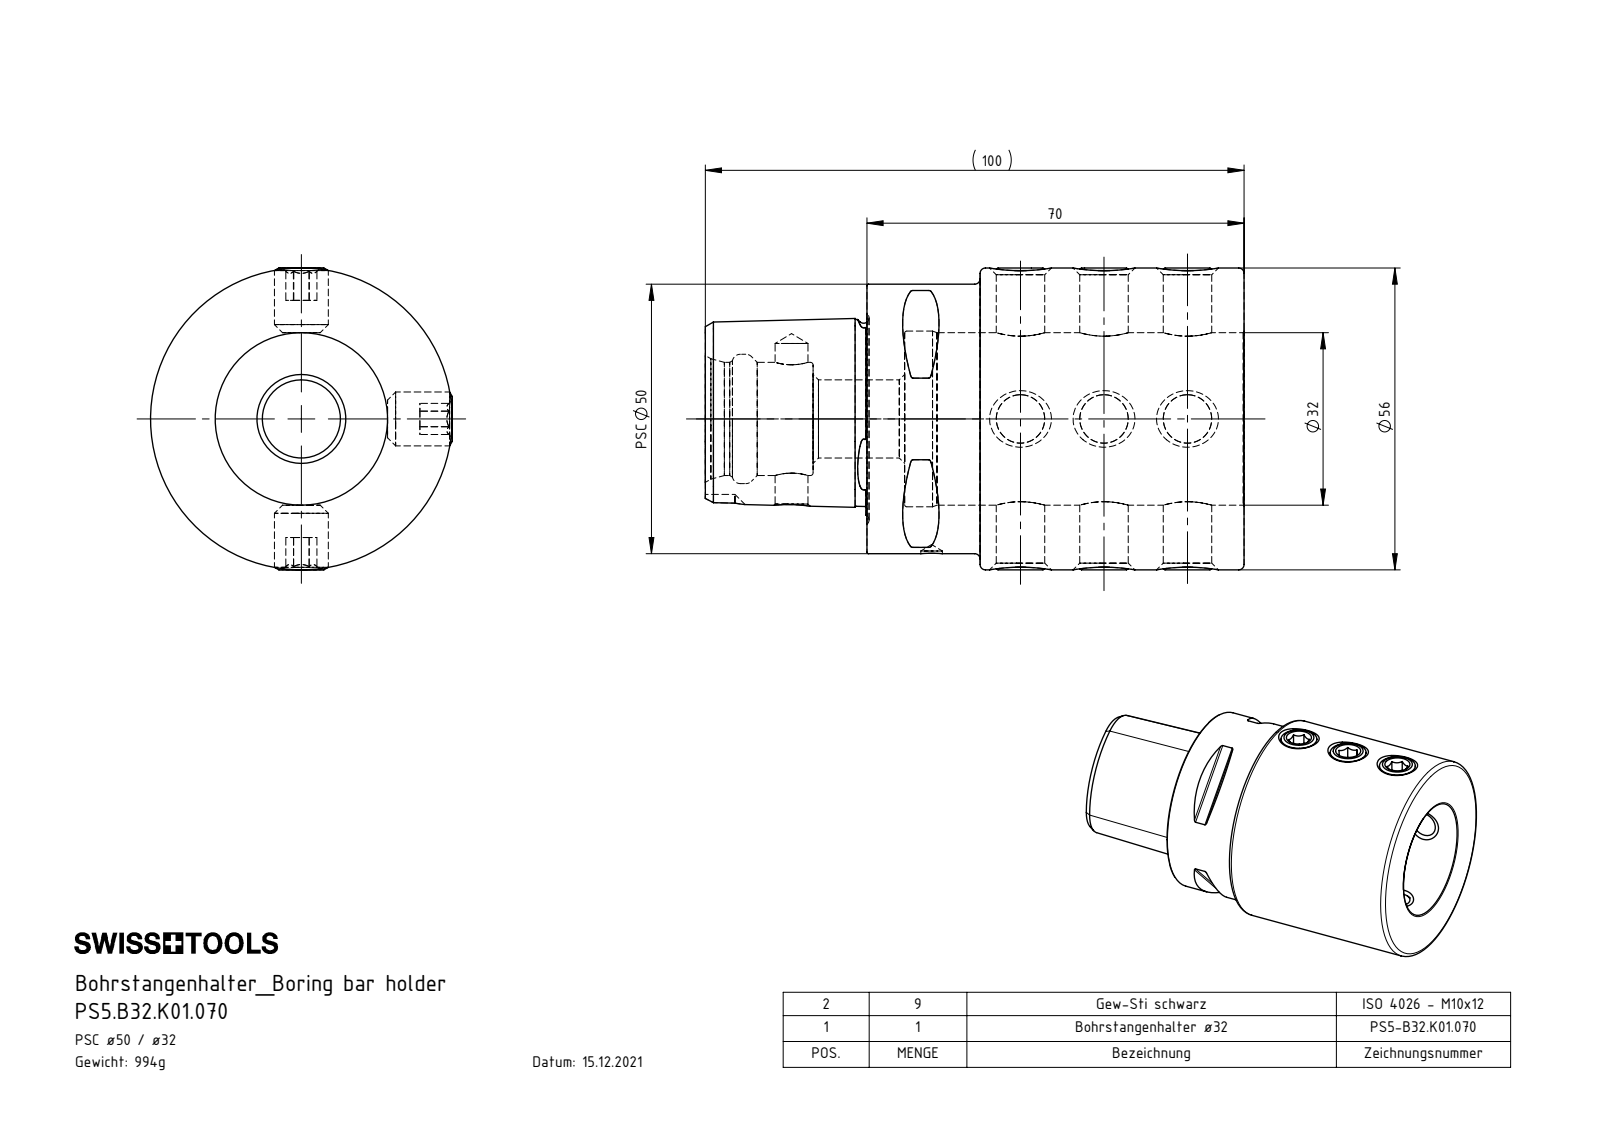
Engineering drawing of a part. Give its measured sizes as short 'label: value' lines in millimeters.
name: ISO 4026 - M10 x 12_PreviewCfg; PS5-B32.K01.070_B; PS5.B32.K01.070
written by: SolidWorks 2017 (AUTOMOTIVE_DESIGN)
unit: mm
bodies: 10 solids, 229 faces (102 planar, 38 cylindrical, 89 other)
size: 100 × 56 × 56
volume: 126 645 mm³; area: 35 258 mm²
holes: 6× ⌀9, 1× ⌀4, 1× ⌀6.1, 1× ⌀14.5, 1× ⌀21, 1× ⌀24, 1× ⌀32, 1× ⌀32.6
bosses: 6× ⌀10, 1× ⌀56, 1× ⌀50
rounds: 8× R0.5, 1× R4
face distances: 70, 7, 63, 5, 30, 37, 100, 6, 19.18, 51
hole spacings: 15.5, 31, 16.5, 26, 32, 42.5, 47.5, 58
